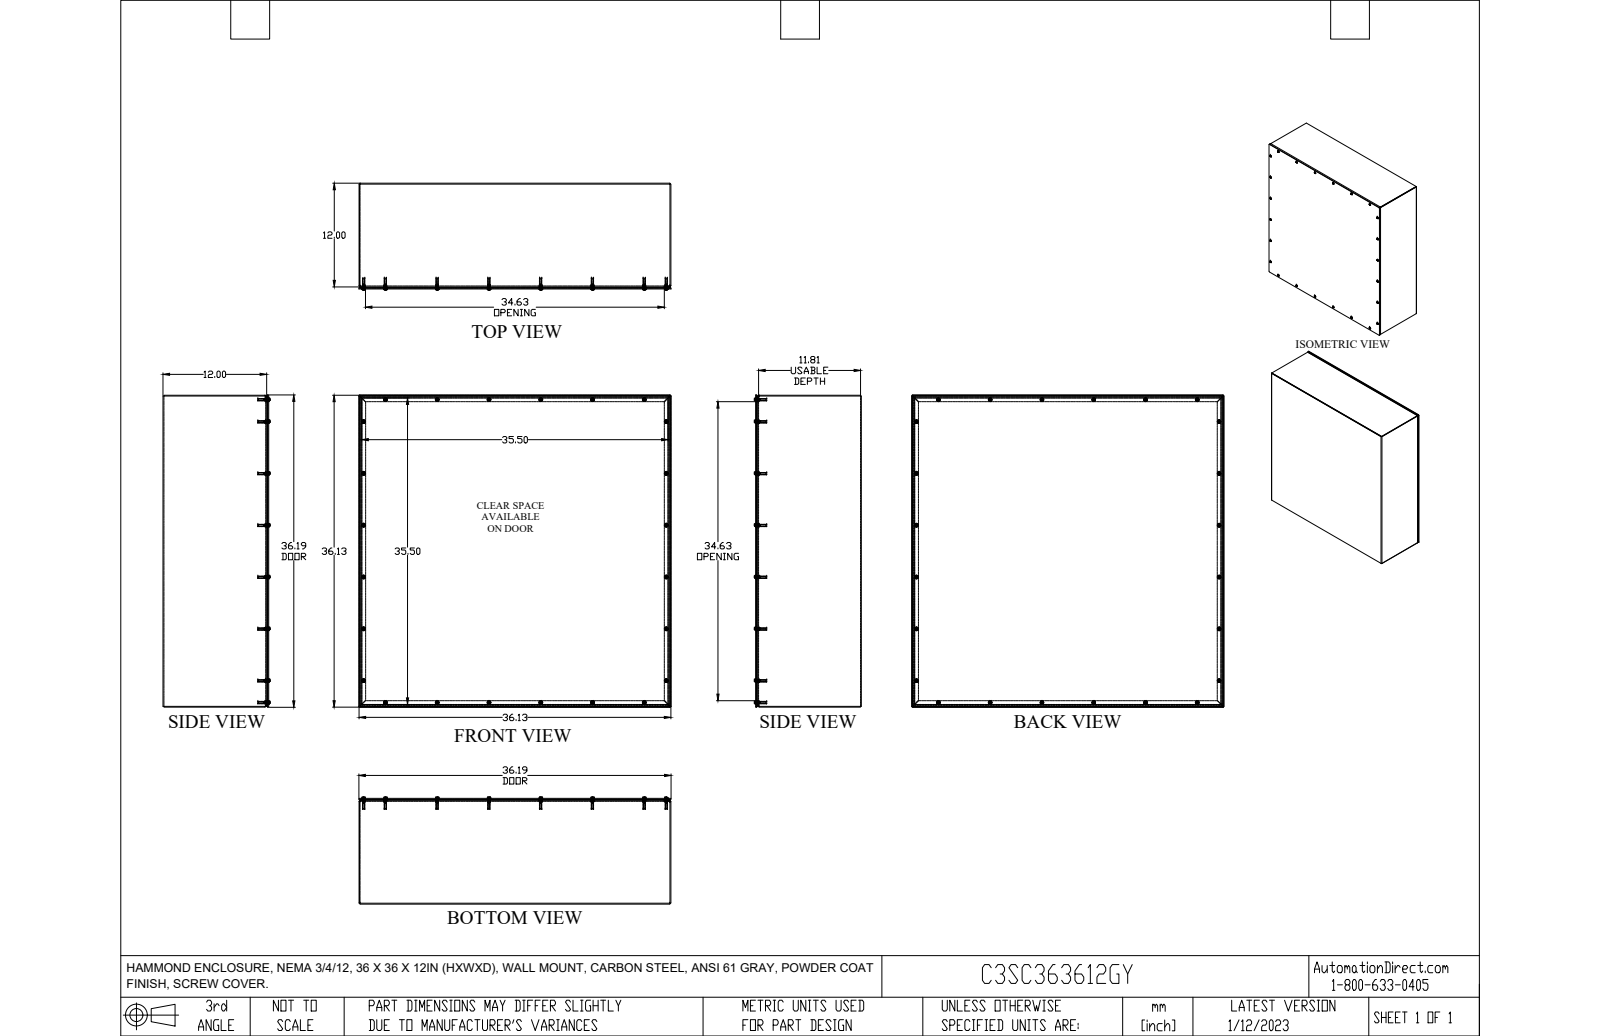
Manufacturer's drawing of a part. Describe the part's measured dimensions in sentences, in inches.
The part is named "C3SC363612GY". Its 3-D file was written by "SolidWorks 2021 (AUTOMOTIVE_DESIGN)". It is 77 solids with 2206 faces: 1382 planar, 388 cylindrical and 436 other. Overall it measures 36.188 by 36.188 by 12.4 inches. Its volume is 462.2 cubic inches and its surface area 9 090 square inches. Round holes: 24 of diameter 0.159, 24 of diameter 0.16, 24 of diameter 0.25. Round bosses or shafts: 24 of diameter 0.44, 24 of diameter 0.39, 24 of diameter 0.24, 24 of diameter 0.19, 24 of diameter 0.148, 20 of diameter 0.275, 4 of diameter 0.275. Partial cylindrical surfaces (rounded edges, fillets, slot ends): 24 of radius 0.16, 8 of radius 0.125, 4 of radius 0.048, 4 of radius 0.126, 4 of radius 0.143, 4 of radius 0.374, 2 of radius 0.095, 2 of radius 0.19. The main face-to-face distances are 0.095, 36.03, 0.095, 0.125, 12.155, 12.03, 12.25, 12.125, 35.935, 36.125. The hole center spacings are 6, 35.584, 12, 37.071, 18, 35.075, 39.424, 8.906.
